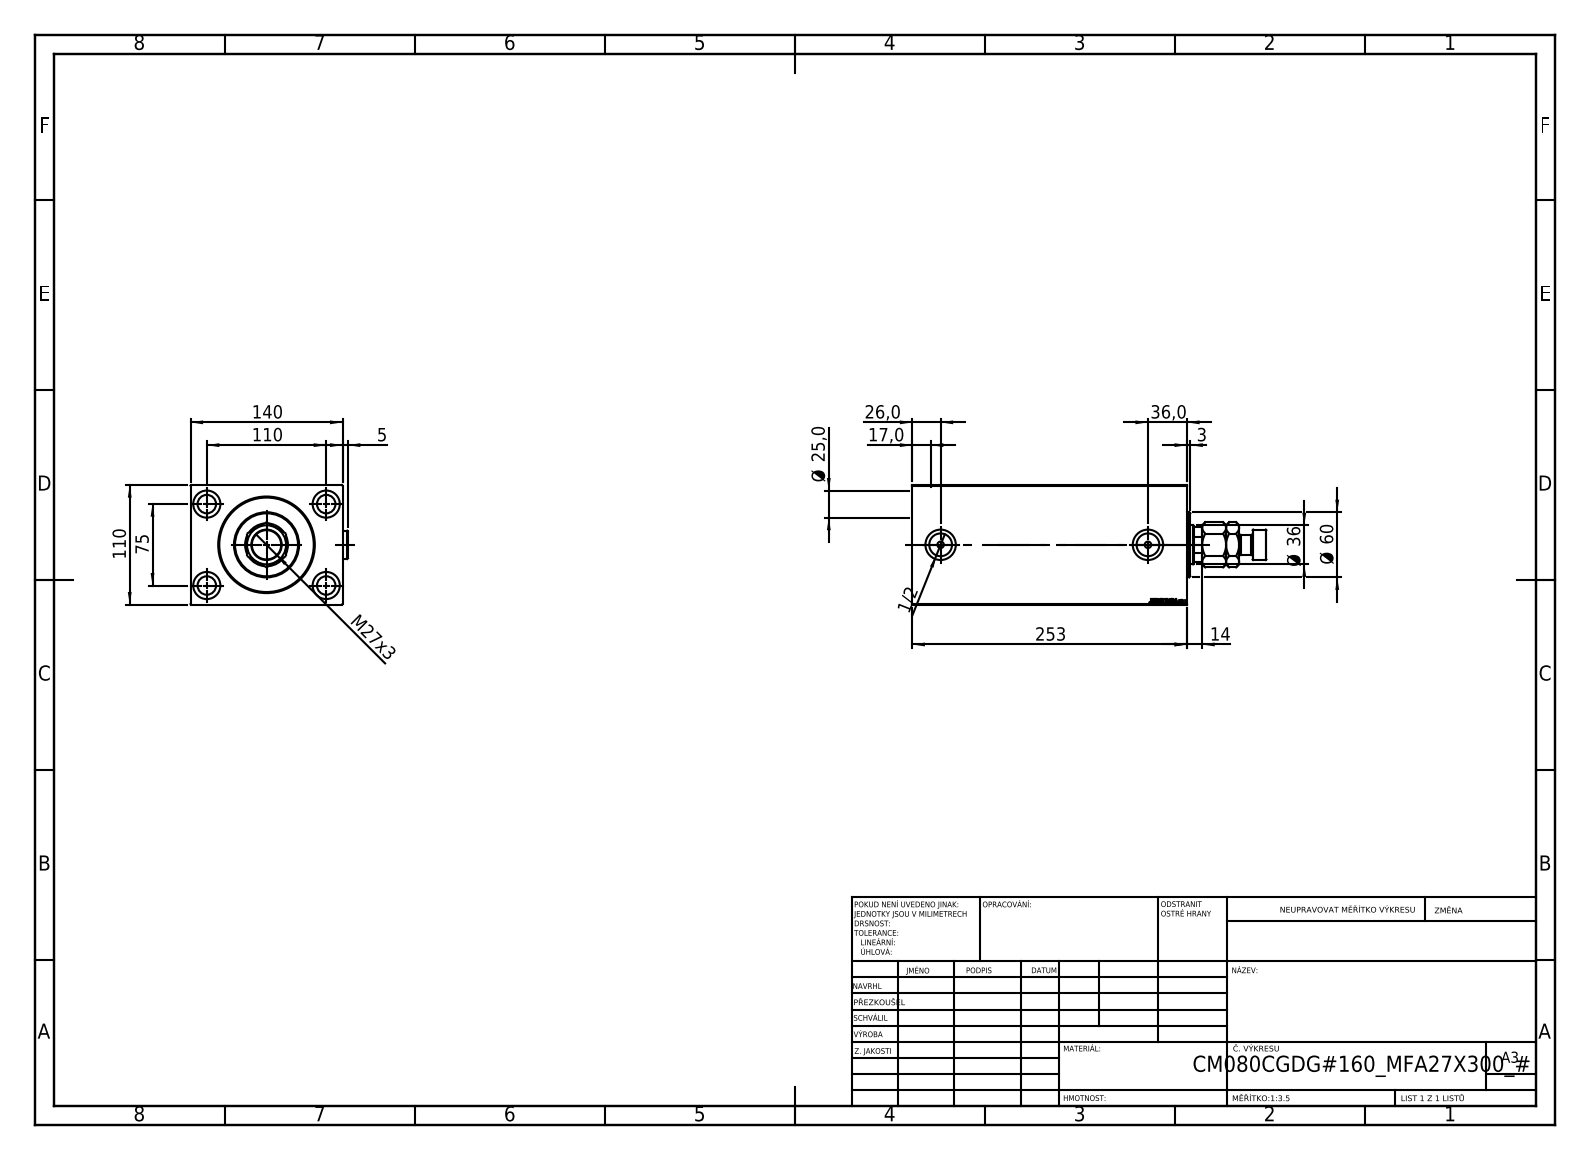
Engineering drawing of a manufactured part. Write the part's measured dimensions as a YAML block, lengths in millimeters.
part_name: "V450CM_VC_B; Zatka_OIL_PORT; V450CM_C_VCP; V450CM_C_Body (+1 more)"
step_written_by: "SolidWorks 2019 (CONFIG_CONTROL_DESIGN)"
units: millimeters
bodies: {solids: 6, faces: 971, planar: 459, cylindrical: 82, other: 430}
overall_size: [326, 144.9, 110]
volume: 3023000
surface_area: 351865
round_holes:
  - {diameter: 17, count: 4}
  - {diameter: 25, count: 4}
  - {diameter: 6, count: 2}
  - {diameter: 20.96, count: 2}
  - {diameter: 28, count: 2}
  - {diameter: 25.5, count: 1}
  - {diameter: 36, count: 1}
  - {diameter: 39.5, count: 1}
  - {diameter: 80, count: 1}
  - {diameter: 82, count: 1}
  - {diameter: 87, count: 1}
round_bosses_or_shafts:
  - {diameter: 26, count: 2}
  - {diameter: 60, count: 1}
  - {diameter: 28, count: 1}
  - {diameter: 18, count: 1}
partial_cylinders:
  - {radius: 17.5, count: 1}
face_to_face_distances: [110, 140, 253, 232, 21, 14, 239, 218, 174, 160]
hole_center_spacings: [66.57, 75, 110, 133.14, 191]
